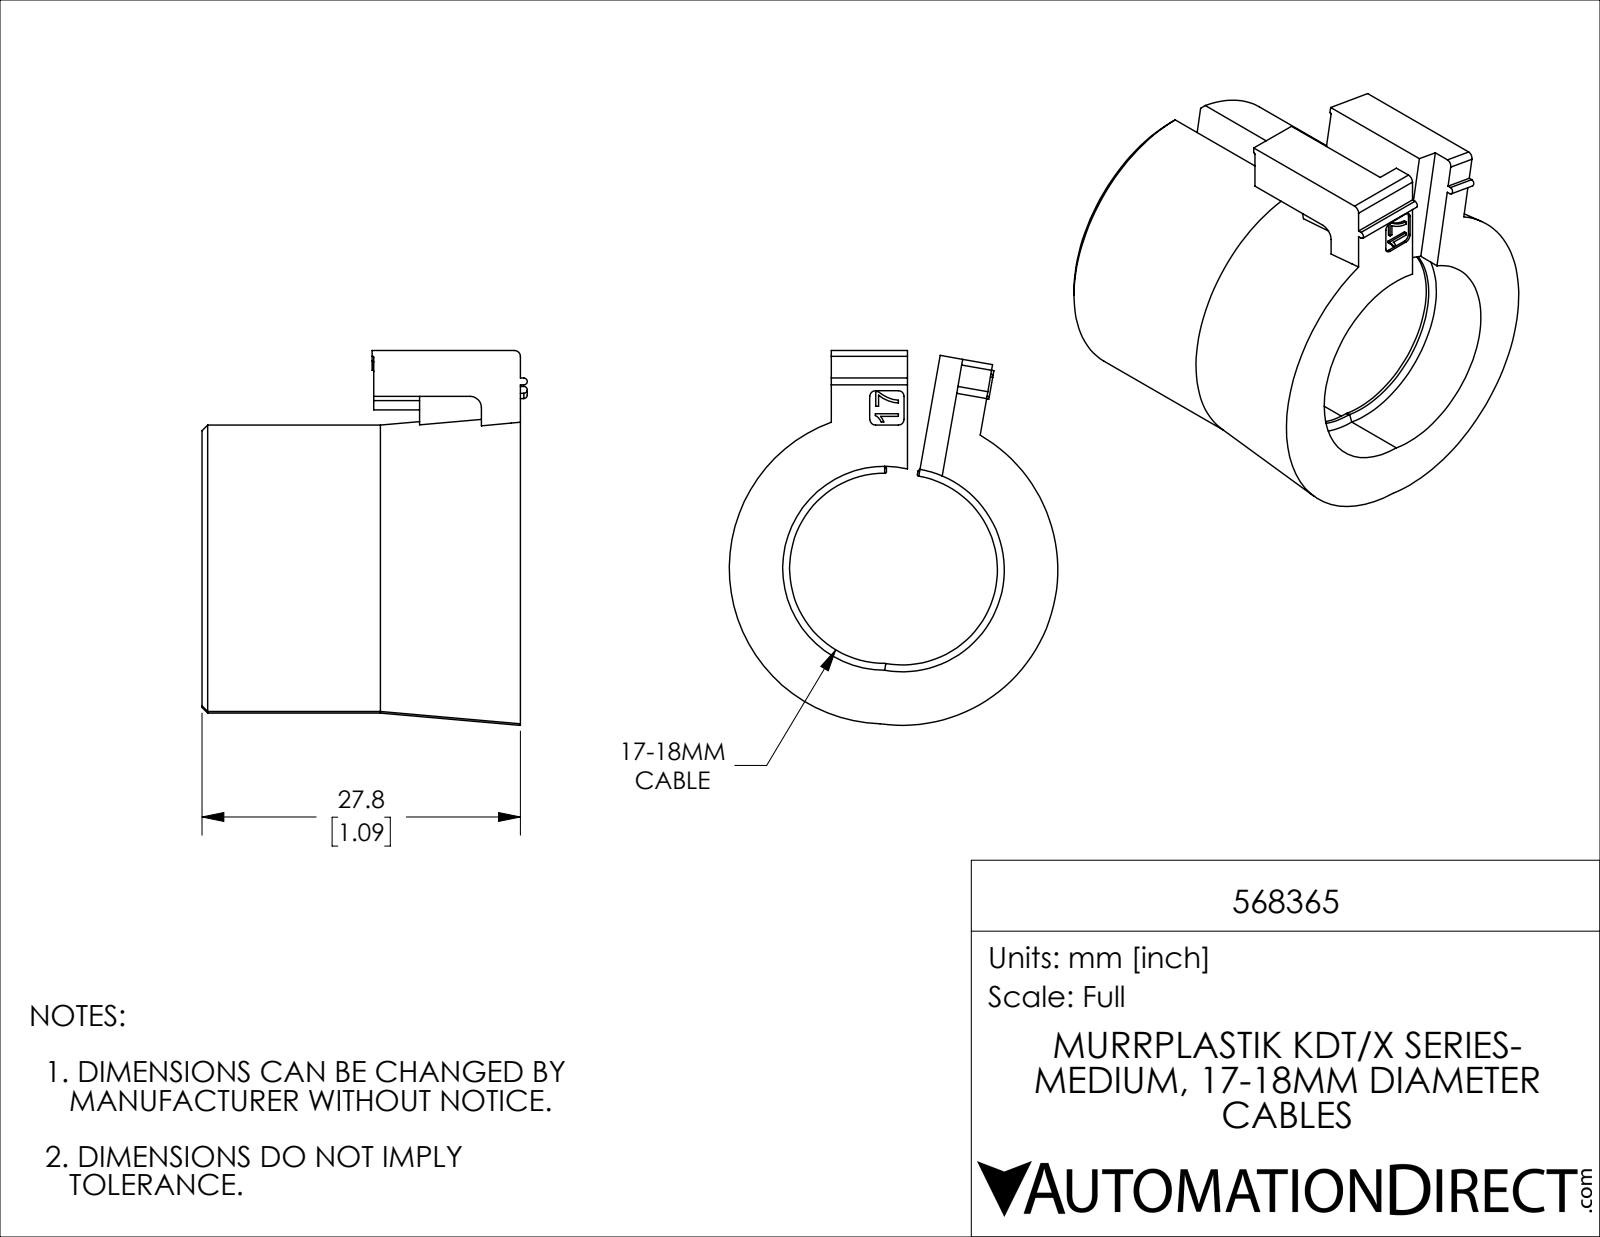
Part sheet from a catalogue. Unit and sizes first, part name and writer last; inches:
Units: inches
Overall size (bounding box): 1.288 × 1.129 × 1.118
Partial cylindrical surfaces — rounded edges, fillets, slot ends (radius × count): R0.004 ×6, R0.02 ×6, R0.012 ×2, R0.039 ×2, R0.327 ×2, R0.35 ×2, R0.492 ×2
Main face-to-face distances: 1.094, 0.157, 0.079, 0.183, 0.183, 1.016, 0.504, 0.425, 0.591, 0.262
Volume: 0.478 in³ · Surface area: 7.931 in²
Bodies: 1 solid, 116 faces (71 planar, 28 cylindrical, 17 other)
Part name (STEP PRODUCT): 568365
STEP written by: SolidWorks 2019 (CONFIG_CONTROL_DESIGN)
